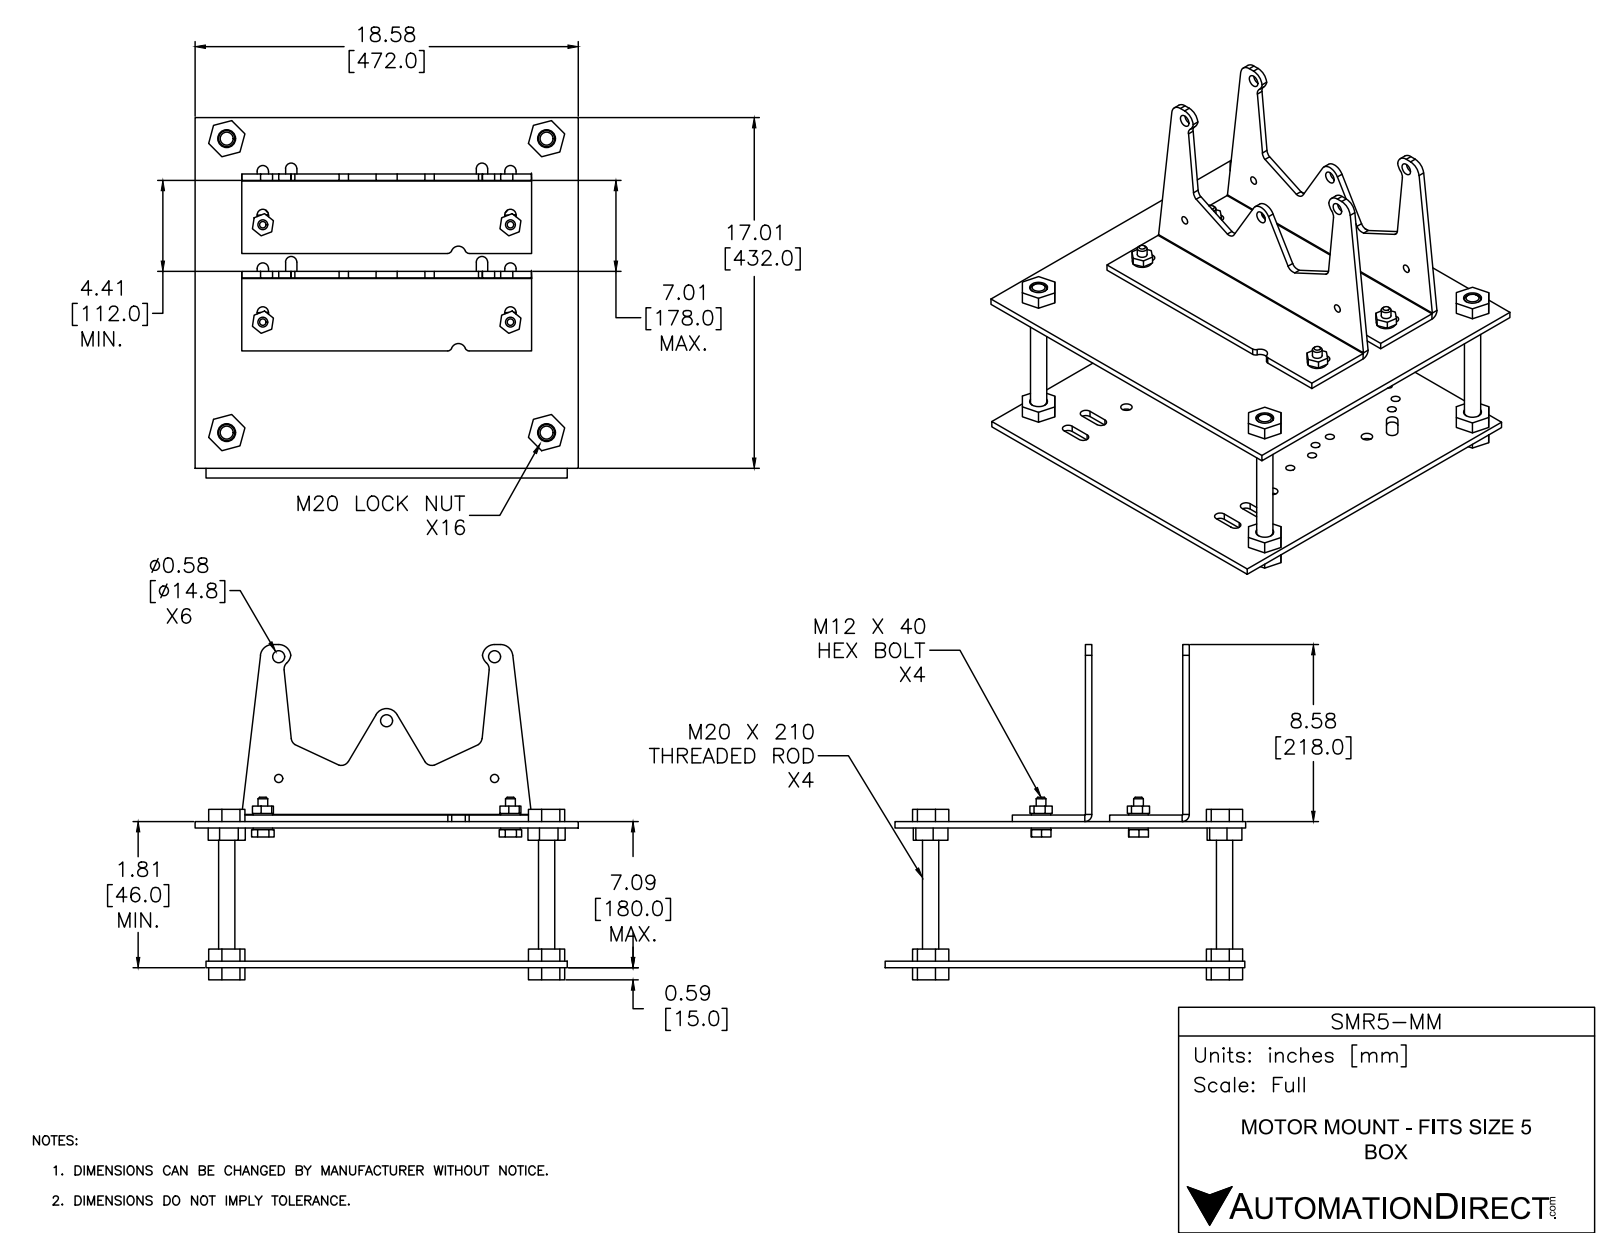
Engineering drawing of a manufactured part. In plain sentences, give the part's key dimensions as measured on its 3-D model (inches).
The part is named "SMR5-MM". Its 3-D file was written by "SolidWorks 2016 (AUTOMOTIVE_DESIGN)". It is 40 solids with 644 faces: 304 planar, 248 cylindrical and 92 other. Overall it measures 18.583 by 17.48 by 16.26 inches. Its volume is 294.8 cubic inches and its surface area 2 030 square inches. Round holes: 12 of diameter 0.433, 4 of diameter 0.472, 4 of diameter 0.551, 4 of diameter 0.787, 4 of diameter 0.807, 4 of diameter 0.827, 3 of diameter 0.374, 3 of diameter 0.583, 2 of diameter 0.394. Round bosses or shafts: 4 of diameter 0.945. Partial cylindrical surfaces (rounded edges, fillets, slot ends): 32 of radius 0.276, 7 of radius 0.591, 6 of radius 0.394, 4 of radius 0.197, 2 of radius 0.029, 2 of radius 0.344, 2 of radius 0.354. The main face-to-face distances are 0.315, 6.772, 7.087, 6.457, 4.724, 7.402, 0.63, 4.409, 5.039, 0.591. The hole center spacings are 10.08, 2.278, 2.591, 7.48, 8.465, 9.875, 0.879, 0.895.
